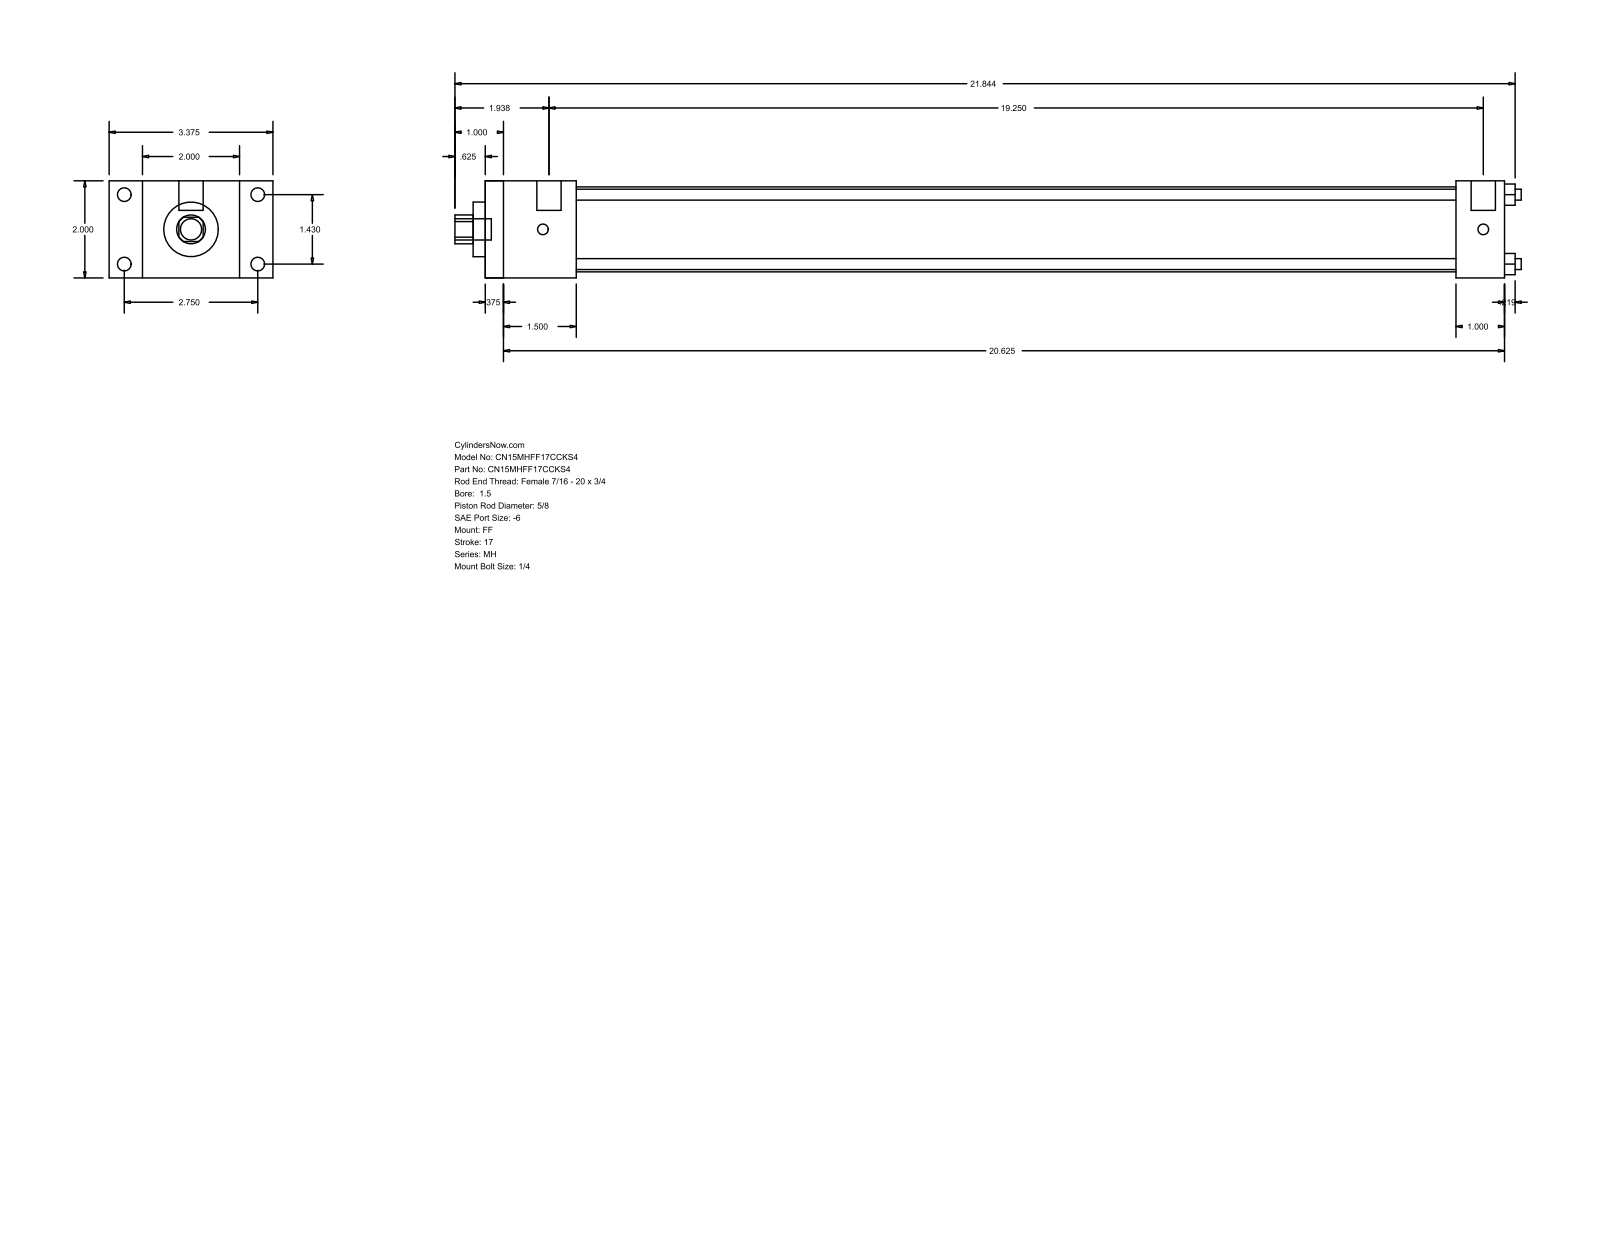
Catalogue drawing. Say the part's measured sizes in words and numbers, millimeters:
The part is named "MH_FF__0150_0.625". Its 3-D file was written by "GSSL Pune (CONFIG_CONTROL_DESIGN)". It is 0 solids with 92 faces: 64 planar, 28 cylindrical and 0 other. Overall it measures 558.01 by 85.72 by 50.8 millimeters. Round holes: 4 of diameter 5.71, 1 of diameter 15.88, 1 of diameter 28.57, 1 of diameter 44.45. Round bosses or shafts: 4 of diameter 7.14, 4 of diameter 5.56, 2 of diameter 12.7, 1 of diameter 11.11. Partial cylindrical surfaces (rounded edges, fillets, slot ends): 1 of radius 7.54. The main face-to-face distances are 50.8, 533.39, 9.52, 523.87, 17.46, 68.26, 47.62, 38.1, 485.77, 508. The hole center spacings are 25.68, 36.32, 51.36.
